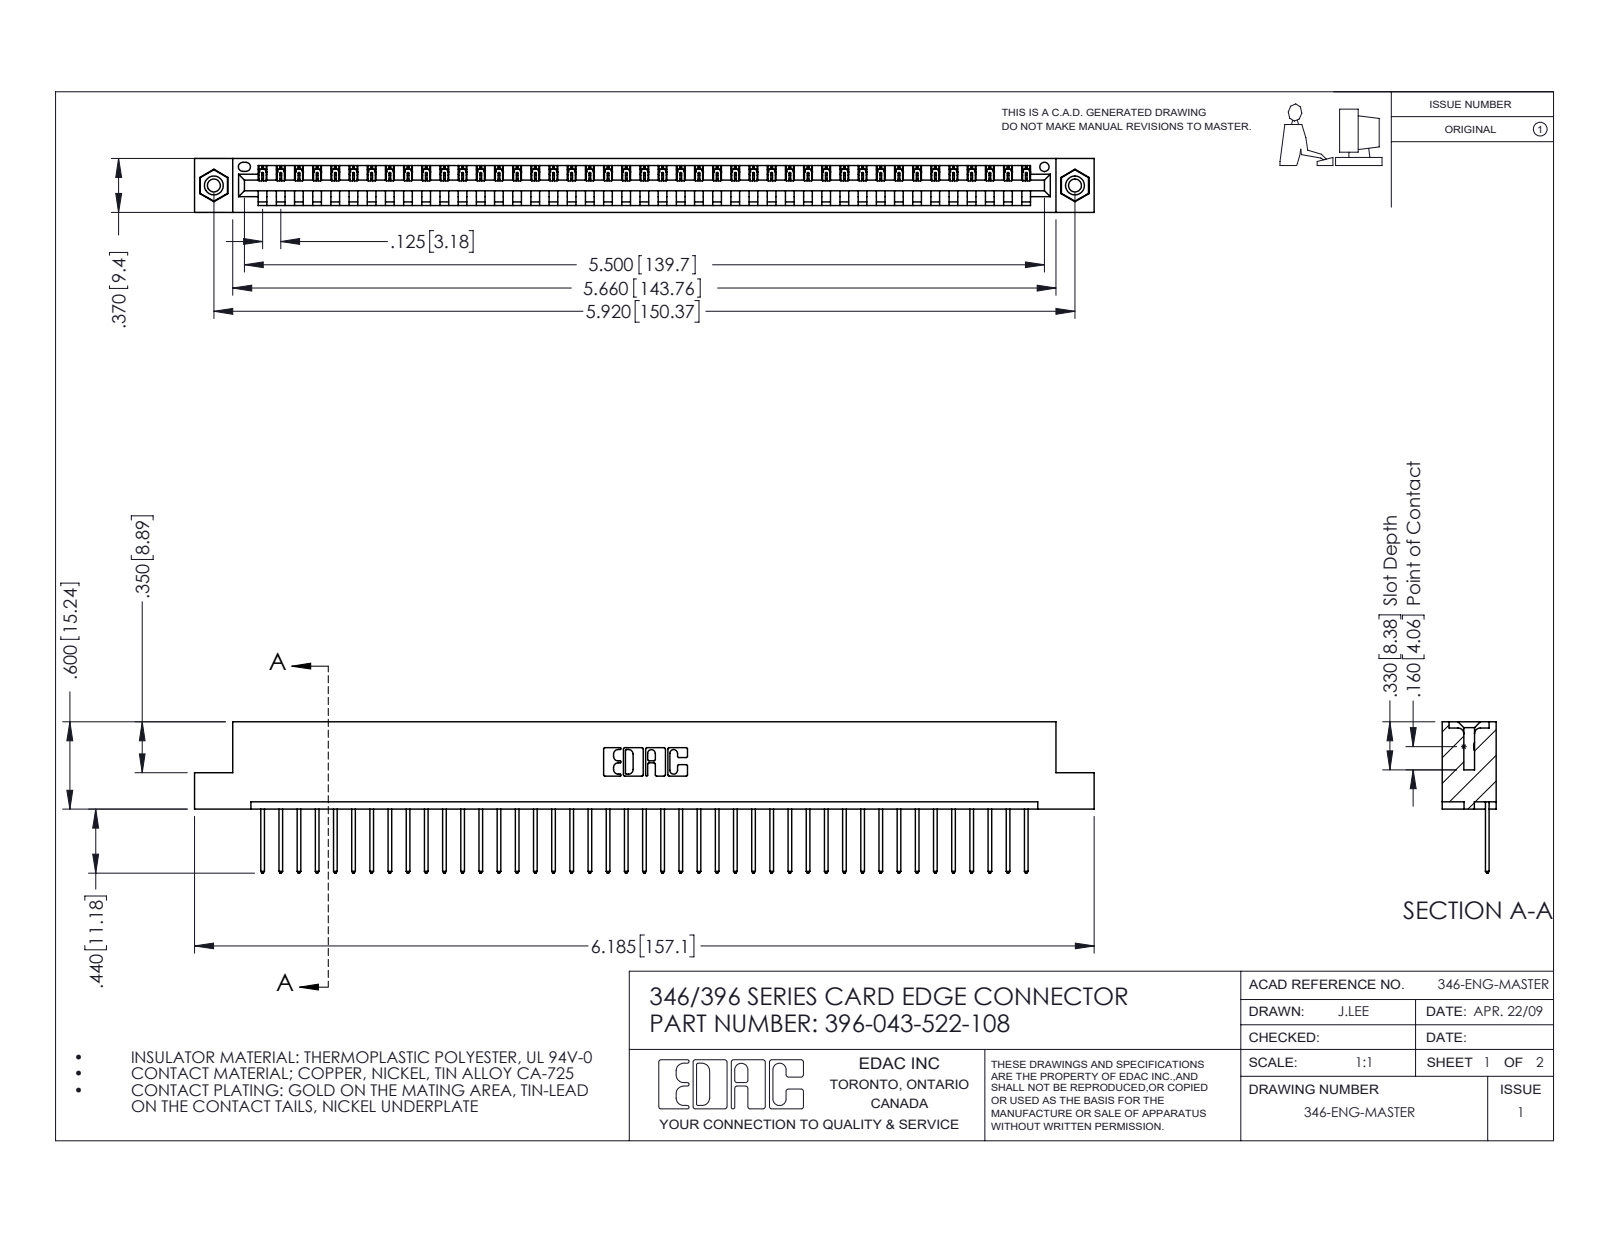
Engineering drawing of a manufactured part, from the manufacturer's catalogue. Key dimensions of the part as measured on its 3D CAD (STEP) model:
Part name (STEP PRODUCT): 345-292-001_345-293-122; 345-250-001_345-250-003-102; 346 Part_Flush Mounting Lugs - 0.156 Dia-TI; 396-043-522-108
STEP written by: SolidWorks 2016 (CONFIG_CONTROL_DESIGN)
Units: inches
Bodies: 46 solids, 2676 faces (1828 planar, 832 cylindrical, 16 other)
Overall size (bounding box): 6.185 × 1.04 × 0.37
Volume: 0.918 in³ · Surface area: 29.44 in²
Round holes (diameter × count): ⌀0.089 ×2, ⌀0.125 ×2, ⌀0.156 ×2, ⌀0.064 ×1
Round bosses / shafts (diameter × count): ⌀0.155 ×2
Partial cylindrical surfaces — rounded edges, fillets, slot ends (radius × count): R0.006 ×86, R0.01 ×86, R0.01 ×22, R0.007 ×6, R0.031 ×6, R0.026 ×3, R0.031 ×2, R0.04 ×2
Main face-to-face distances: 0.048, 0.322, 0.37, 0.25, 0.072, 0.298, 0.025, 0.148, 0.222, 0.1
Hole centre spacings: 0.246, 5.711, 5.92
